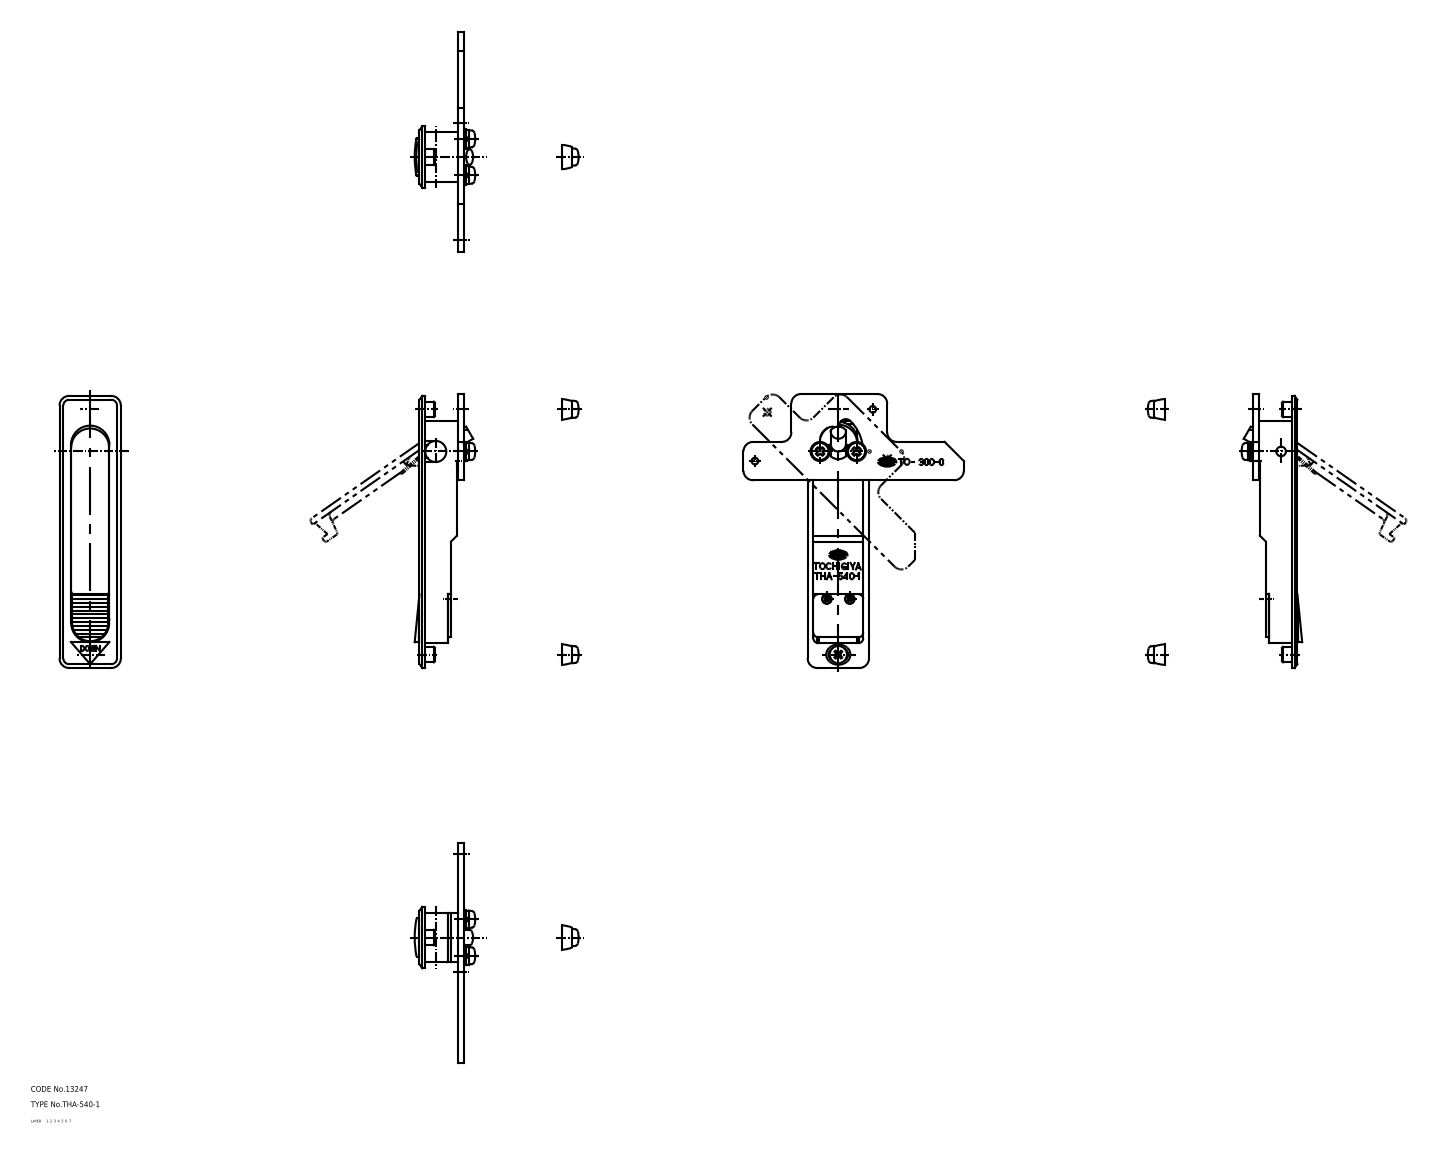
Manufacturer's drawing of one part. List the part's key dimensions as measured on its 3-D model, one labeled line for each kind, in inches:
Part name (STEP PRODUCT): screw_A; bracket; screw_B; latch (+5 more)
STEP written by: CADfix (AUTOMOTIVE_DESIGN)
Units: inches
Bodies: 11 solids, 423 faces (0 planar, 0 cylindrical, 423 other)
Overall size (bounding box): 5.63 × 4.528 × 1.241
Volume: 3.48 in³ · Surface area: 56.5 in²
